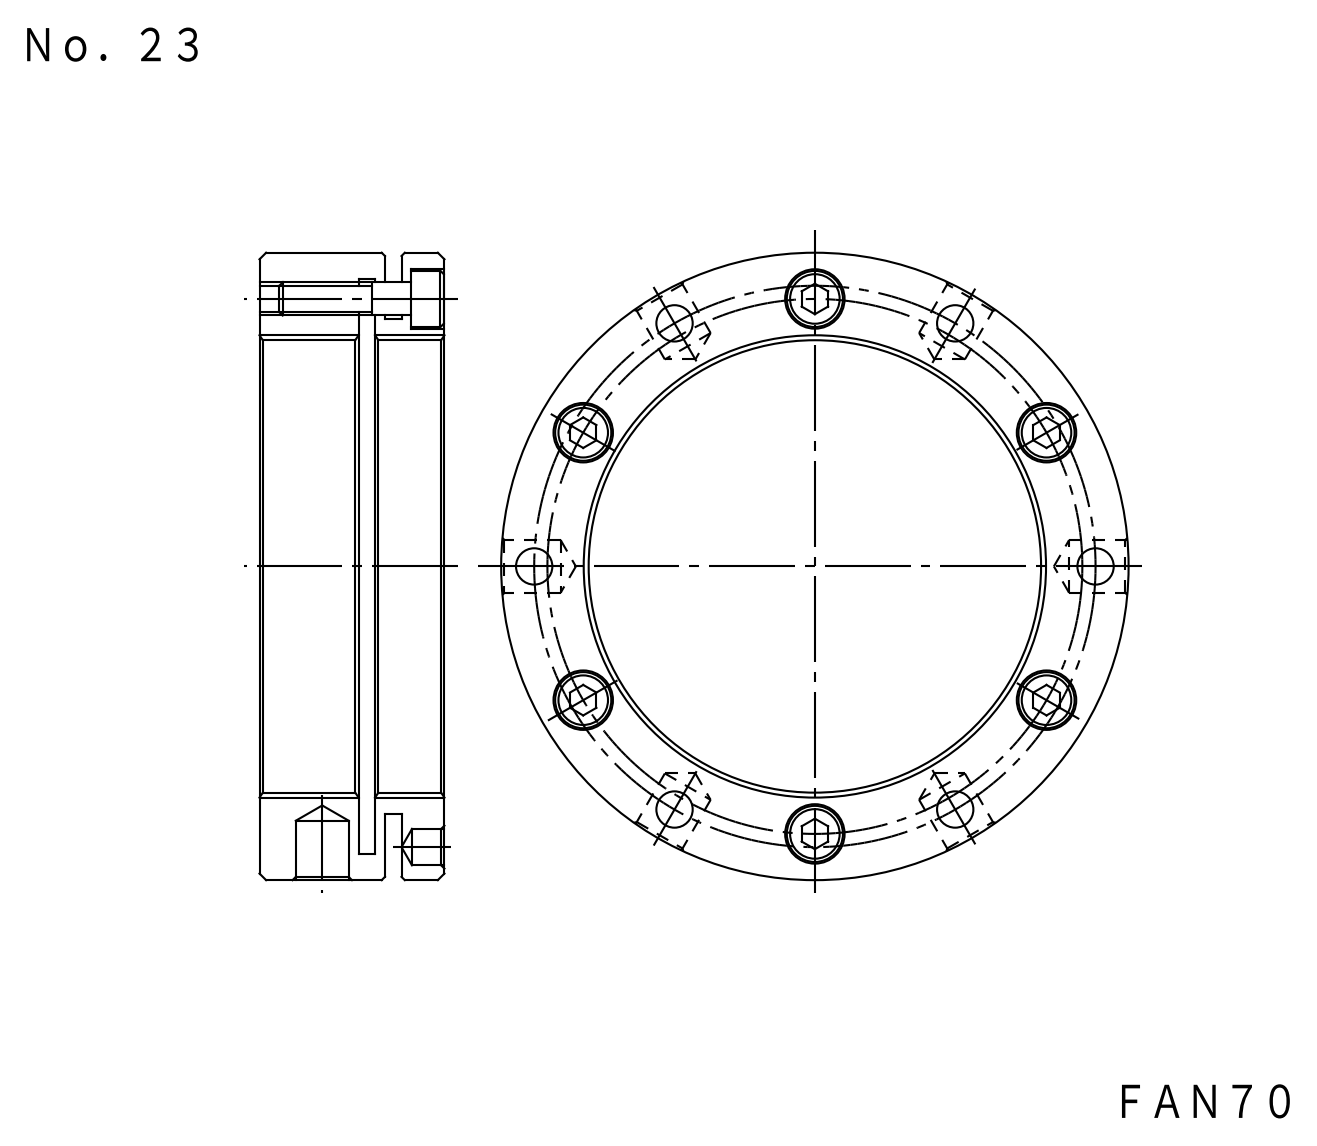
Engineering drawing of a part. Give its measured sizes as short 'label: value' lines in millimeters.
name: FKD FAN70; M5X20_default
written by: SolidWorks 2012 (CONFIG_CONTROL_DESIGN)
unit: mm
bodies: 7 solids, 204 faces (72 planar, 108 cylindrical, 24 other)
size: 95 × 95 × 28
volume: 75 597 mm³; area: 37 526 mm²
holes: 6× ⌀4.13, 6× ⌀5.3, 6× ⌀5.5, 6× ⌀9, 3× ⌀8, 1× ⌀70, 1× ⌀88
bosses: 6× ⌀8.5, 6× ⌀5, 1× ⌀95, 1× ⌀76
face distances: 2.5, 4, 14, 28, 18, 10, 20.5, 7.5, 6.5, 16.5
hole spacings: 21.66, 41, 42.5, 80.66, 59.06, 71.02, 59.05, 73.61
